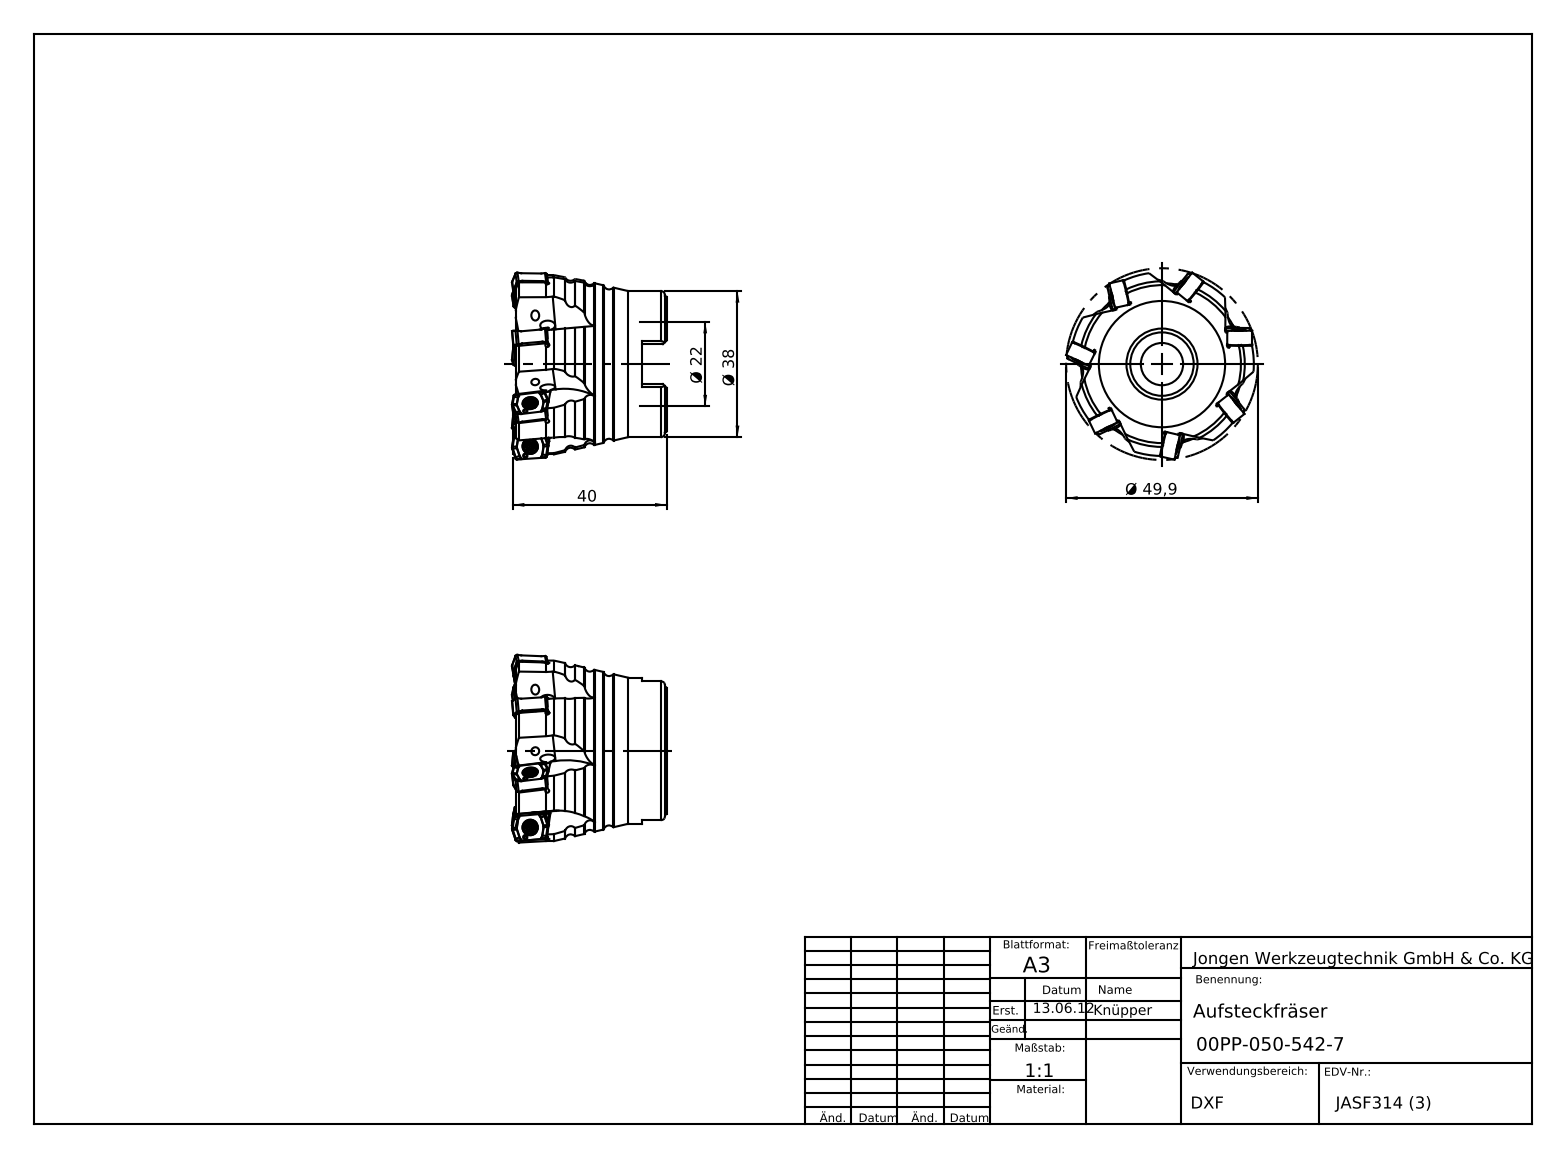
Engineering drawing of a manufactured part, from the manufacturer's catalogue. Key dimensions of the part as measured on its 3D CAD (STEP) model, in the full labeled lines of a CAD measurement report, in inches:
Part name (STEP PRODUCT): 00PP-050-542-7
STEP written by: SolidWorks 2013 (AUTOMOTIVE_DESIGN)
Units: inches
Bodies: 1 solid, 272 faces (129 planar, 34 cylindrical, 109 other)
Overall size (bounding box): 1.849 × 1.838 × 1.517
Volume: 2.09 in³ · Surface area: 16.7 in²
Round holes (diameter × count): ⌀0.098 ×7, ⌀0.433 ×1, ⌀0.65 ×1, ⌀0.866 ×1, ⌀0.872 ×1, ⌀0.878 ×1
Round bosses / shafts (diameter × count): ⌀1.496 ×1
Partial cylindrical surfaces — rounded edges, fillets, slot ends (radius × count): R0.591 ×7, R0.925 ×1
Main face-to-face distances: 1.488, 0.248, 1.24, 0.785, 0.537, 0.703, 1.055, 0.807, 0.27, 0.433
